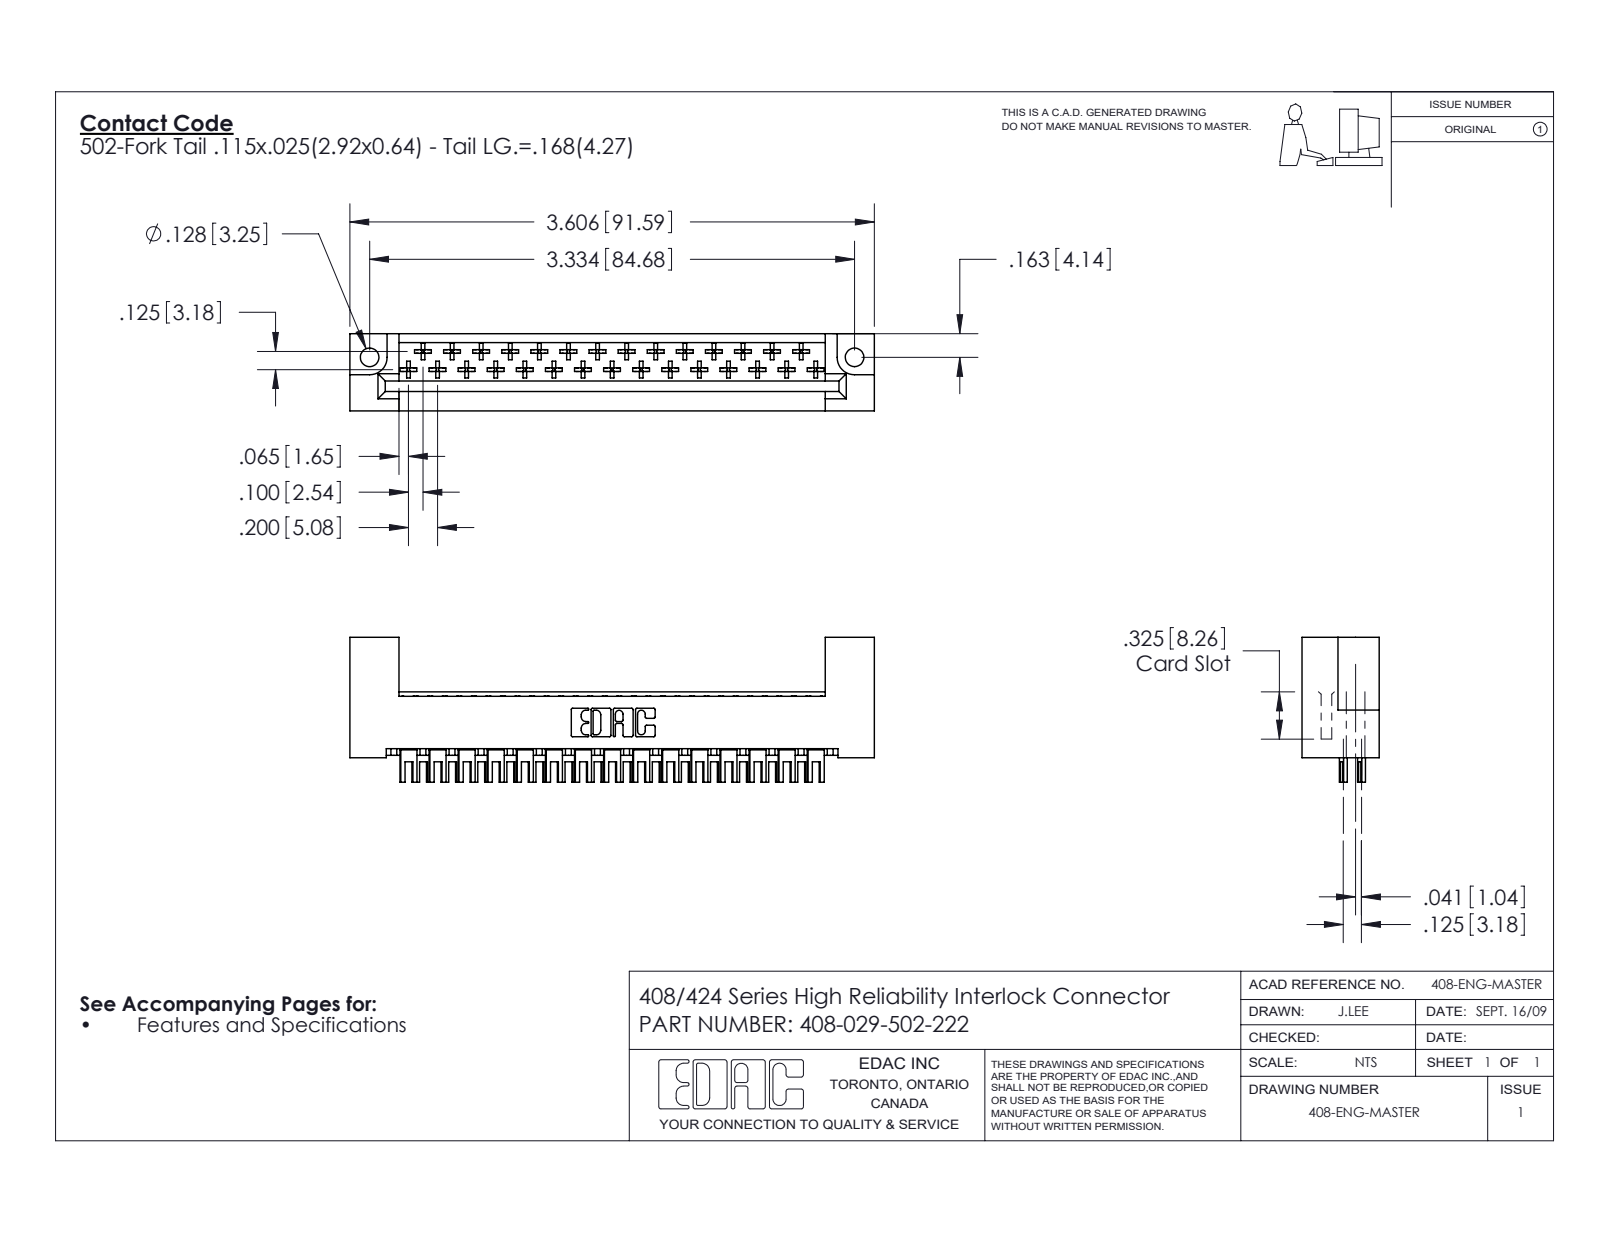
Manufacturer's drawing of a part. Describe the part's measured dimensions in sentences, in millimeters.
The part is named "408-029-502-222; 408-290-001_408-290-102; 408 Part_029 - 2". Its 3-D file was written by "SolidWorks 2016 (CONFIG_CONTROL_DESIGN)". It is 30 solids with 1676 faces: 1278 planar, 282 cylindrical and 116 other. Overall it measures 91.6 by 25.3 by 13.5 millimeters. Its volume is 11 700 cubic millimeters and its surface area 13 480 square millimeters. Round holes: 2 of diameter 3.3. Partial cylindrical surfaces (rounded edges, fillets, slot ends): 174 of radius 0.3, 31 of radius 0.5, 22 of radius 0.3, 6 of radius 0.2, 6 of radius 0.8, 3 of radius 0.7, 2 of radius 3. The main face-to-face distances are 13.5, 3.2, 2.5, 0.6, 0.6, 9.2, 6, 6.6, 5.5, 6.9. The hole center spacings are 84.7.
